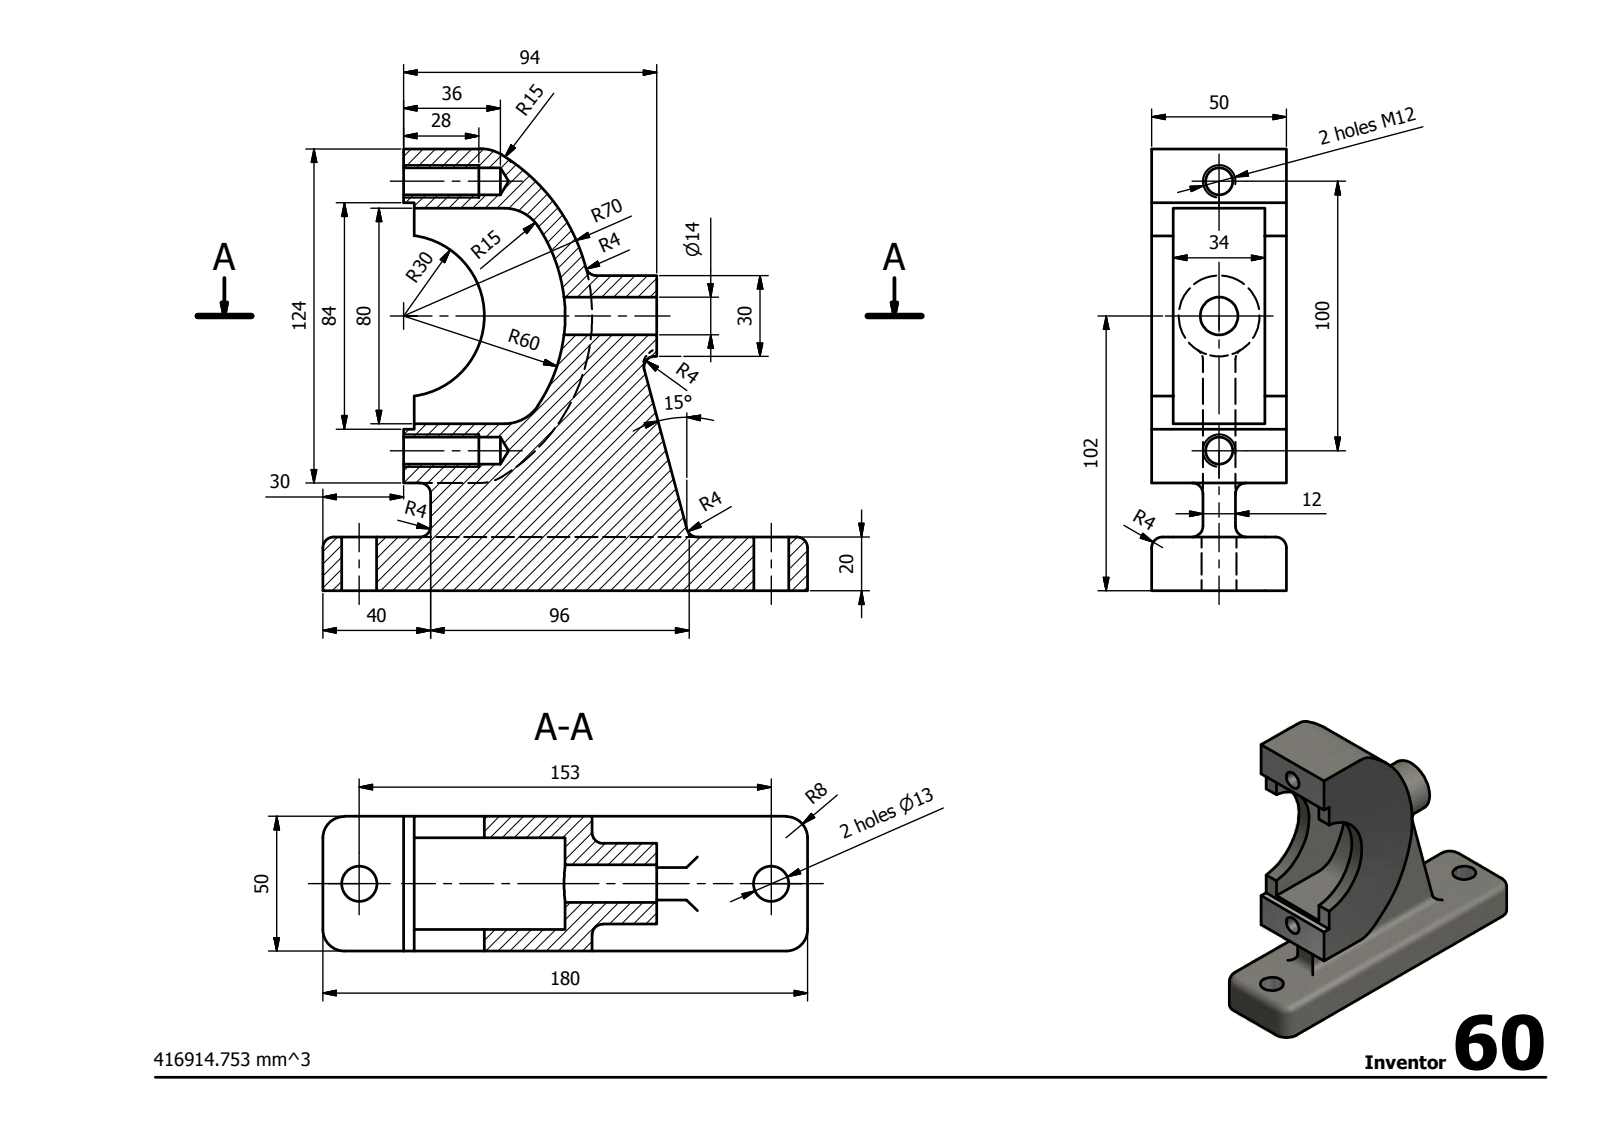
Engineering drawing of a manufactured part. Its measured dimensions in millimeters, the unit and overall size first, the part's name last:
Units: millimetres
Overall size (bounding box): 180 × 164 × 50
Round holes (diameter × count): ⌀10.11 ×2, ⌀13 ×2, ⌀14 ×1
Round bosses / shafts (diameter × count): ⌀30 ×1
Partial cylindrical surfaces — rounded edges, fillets, slot ends (radius × count): R4 ×13, R8 ×4, R15 ×4, R30 ×1, R60 ×1, R70 ×1
Main face-to-face distances: 50, 42, 20, 19, 31, 8, 11, 23, 34, 12
Hole centre spacings: 50, 100, 153
Volume: 416 896 mm³ · Surface area: 76 557 mm²
Bodies: 1 solid, 71 faces (25 planar, 32 cylindrical, 14 other)
STEP written by: Autodesk Inventor 2014 (AUTOMOTIVE_DESIGN)
